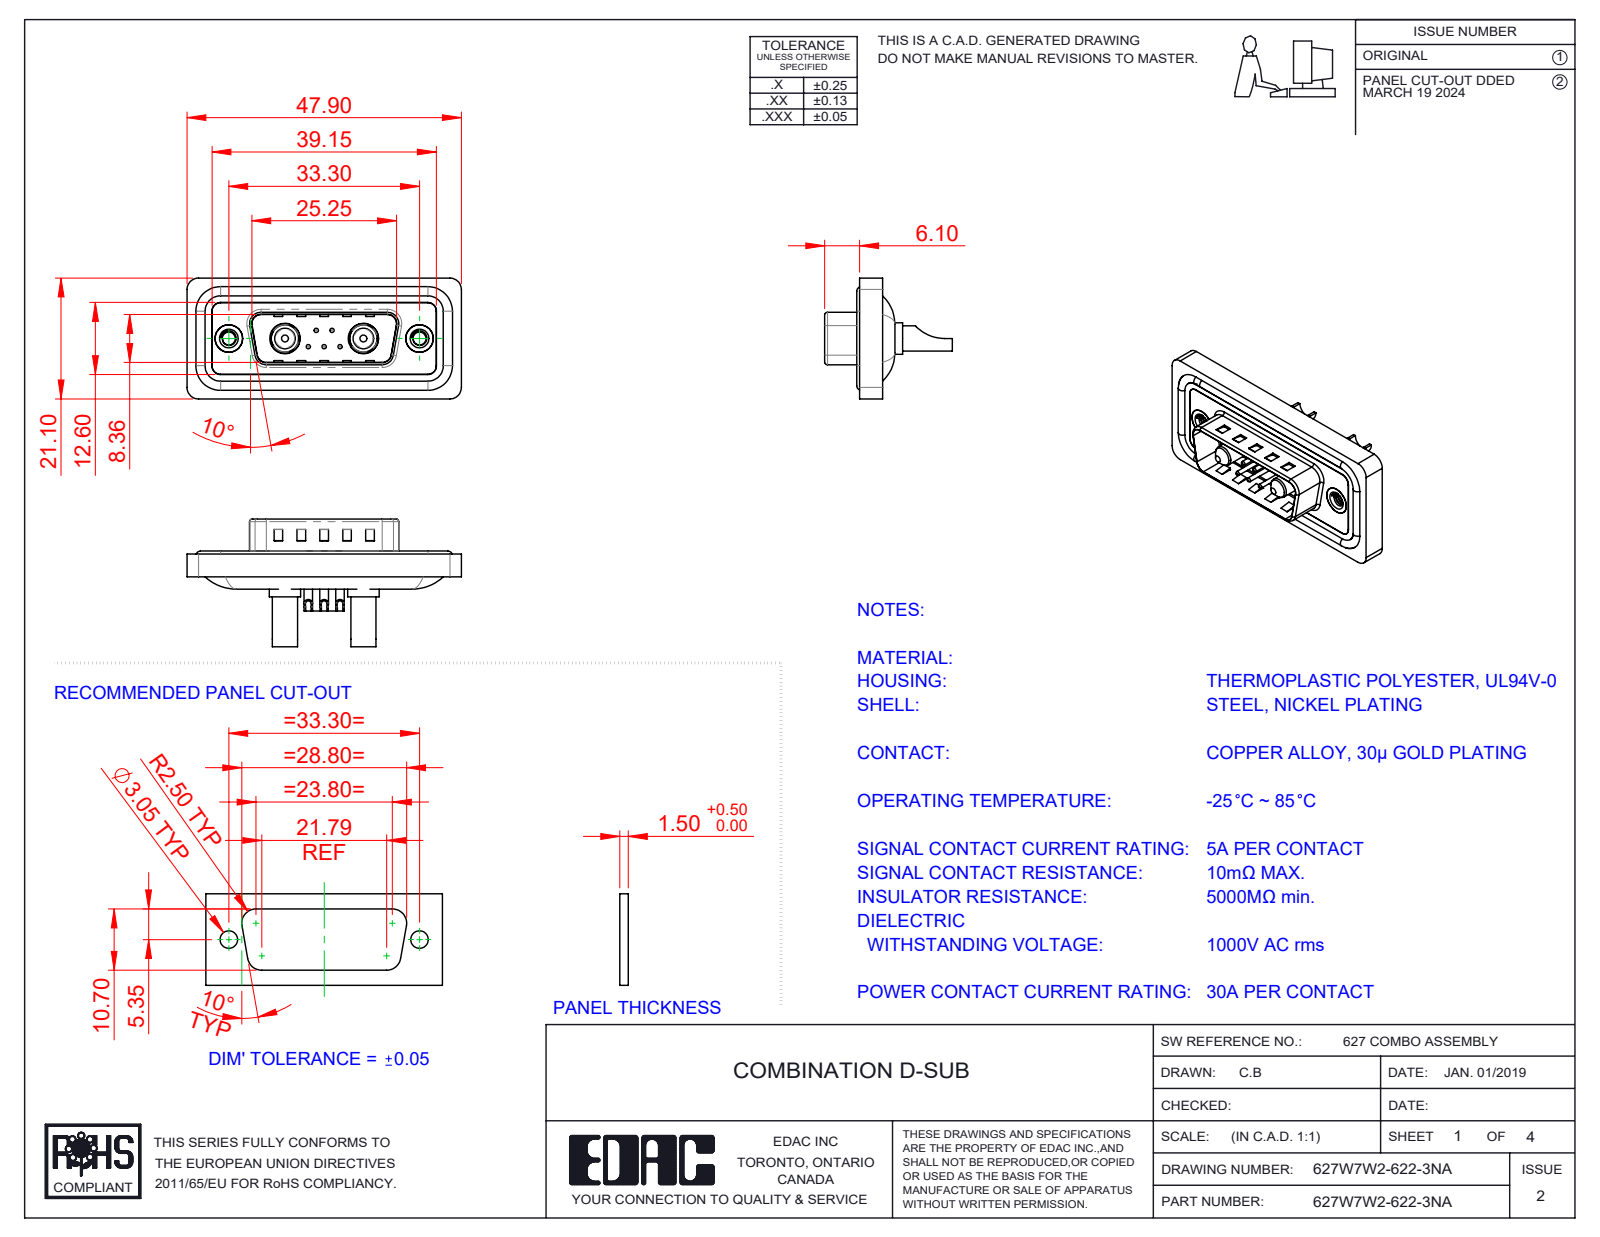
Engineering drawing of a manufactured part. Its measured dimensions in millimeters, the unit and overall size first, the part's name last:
Units: millimetres
Overall size (bounding box): 47.9 × 22.3 × 21.1
Round holes (diameter × count): ⌀0.75 ×5, ⌀1 ×5, ⌀1.6 ×5, ⌀2 ×5, ⌀2.26 ×2, ⌀3.5 ×2, ⌀4 ×2, ⌀4.8 ×2, ⌀4.85 ×2, ⌀5 ×2, ⌀5.3 ×2
Round bosses / shafts (diameter × count): ⌀1.5 ×5, ⌀1.6 ×4, ⌀5.5 ×2, ⌀5.2 ×2, ⌀4.9 ×2, ⌀4.75 ×2, ⌀4.4 ×2, ⌀3.75 ×2
Partial cylindrical surfaces — rounded edges, fillets, slot ends (radius × count): R1.5 ×26, R2 ×20, R0.5 ×8, R1.6 ×8, R1 ×6, R0.25 ×4, R0.6 ×4, R0.65 ×4
Main face-to-face distances: 0.4, 1.1, 1.6, 1.5, 0.5, 3.1, 2.9, 0.82, 9.58, 2.5
Hole centre spacings: 3.16, 2.77, 9.8, 23.5, 4.31, 4.33, 5.03, 5.04
Volume: 5 574 mm³ · Surface area: 9 045 mm²
Bodies: 16 solids, 720 faces (248 planar, 310 cylindrical, 162 other)
Part name (STEP PRODUCT): 627Combo Housing_7W2; 627Combo Contact Row 2_22; 627W7W2-622-3NA; 627Combo Waterproof Housing_15 Contacts (+5 more)
STEP written by: SolidWorks 2023 (CONFIG_CONTROL_DESIGN)
